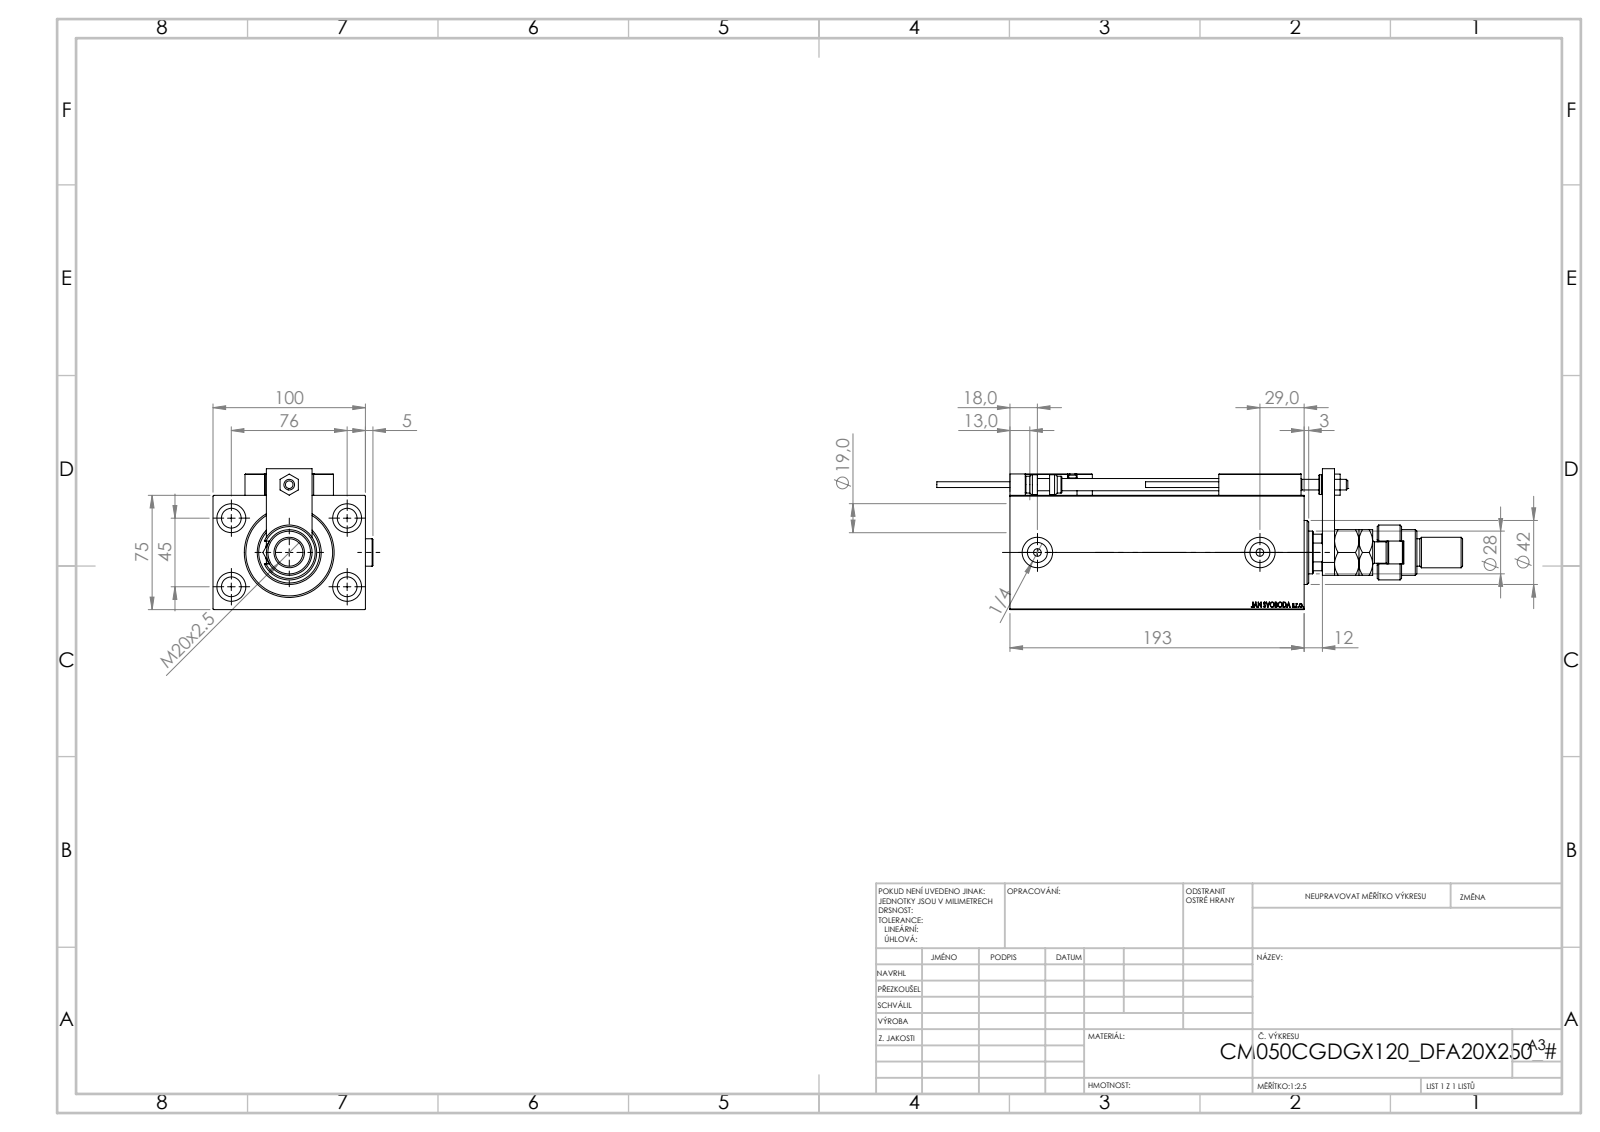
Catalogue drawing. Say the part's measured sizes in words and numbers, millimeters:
The part is named "FEMALE_PART_FOR_DFA; SWITCH_X_FRONT_BACK; MAGNET; V450CM_C_Body (+7 more)". Its 3-D file was written by "SolidWorks 2019 (CONFIG_CONTROL_DESIGN)". It is 27 solids with 1424 faces: 623 planar, 219 cylindrical and 582 other. Overall it measures 345 by 104.9 by 92.5 millimeters. Its volume is 1 272 000 cubic millimeters and its surface area 222 798 square millimeters. Round holes: 5 of diameter 8, 4 of diameter 3.2, 4 of diameter 4, 4 of diameter 5, 4 of diameter 13, 4 of diameter 19, 3 of diameter 20, 2 of diameter 13.16, 1 of diameter 7, 1 of diameter 18.5, 1 of diameter 28, 1 of diameter 31.5. Round bosses or shafts: 3 of diameter 18, 2 of diameter 5, 2 of diameter 3.8, 1 of diameter 42, 1 of diameter 36, 1 of diameter 30, 1 of diameter 22, 1 of diameter 14. Partial cylindrical surfaces (rounded edges, fillets, slot ends): 30 of radius 0.3, 2 of radius 3, 1 of radius 7.5, 1 of radius 12, 1 of radius 13.5. The main face-to-face distances are 75, 100, 14, 193, 12, 179, 20, 8, 24, 25. The hole center spacings are 44.16, 11.37, 20, 29.59, 29.69, 36.06, 42.19, 43.91.
